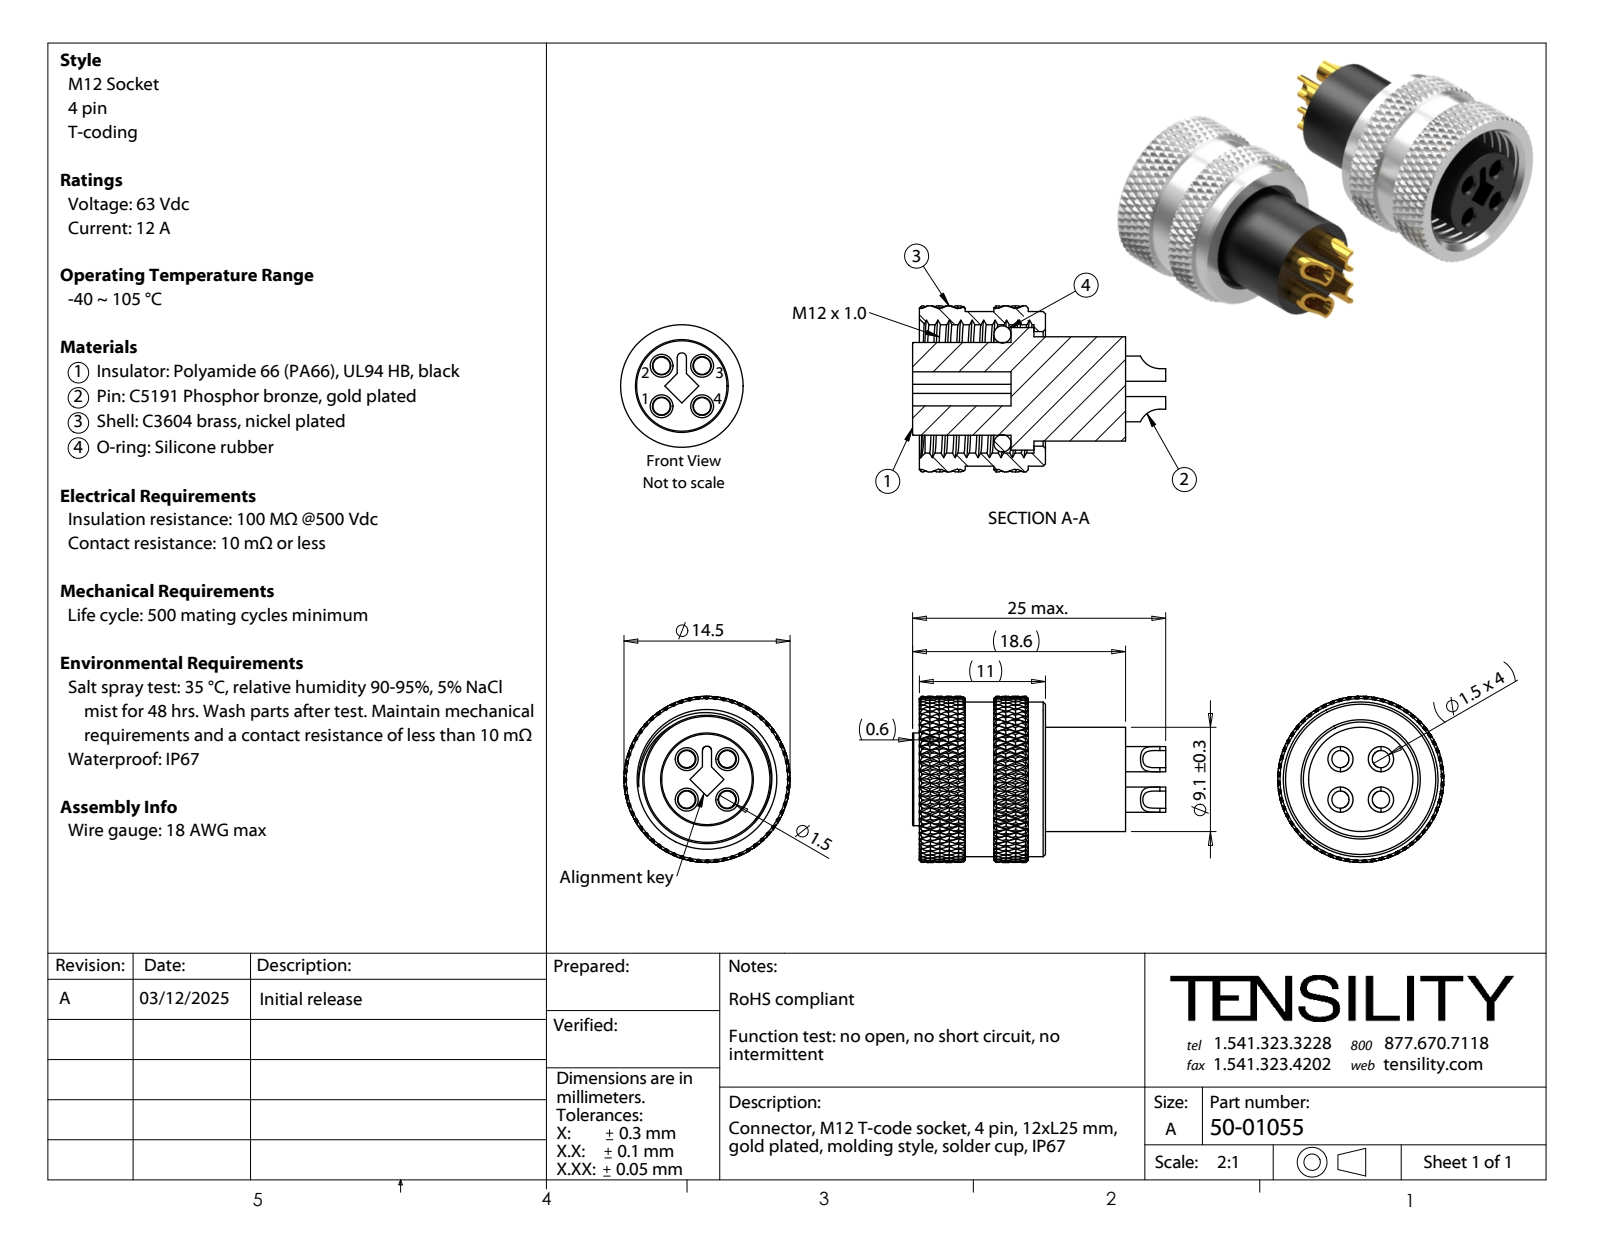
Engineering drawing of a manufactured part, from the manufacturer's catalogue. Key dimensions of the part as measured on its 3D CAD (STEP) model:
Part name (STEP PRODUCT): 50-01055-03; 50-01055-02_step; 50-01055-01; 50-01055 (+1 more)
STEP written by: SolidWorks 2021 (CONFIG_CONTROL_DESIGN)
Units: millimetres
Bodies: 7 solids, 233 faces (74 planar, 97 cylindrical, 62 other)
Overall size (bounding box): 22.1 × 14.5 × 14.5
Volume: 1 718 mm³ · Surface area: 3 338 mm²
Round holes (diameter × count): ⌀1.5 ×4, ⌀1.6 ×4, ⌀10 ×1, ⌀11.2 ×1
Round bosses / shafts (diameter × count): ⌀2.2 ×4, ⌀14.5 ×1, ⌀13.5 ×1, ⌀10.7 ×1, ⌀9.1 ×1, ⌀8.1 ×1
Partial cylindrical surfaces — rounded edges, fillets, slot ends (radius × count): R1.86 ×2, R0.4 ×1
Main face-to-face distances: 8, 10, 2, 7, 3, 1, 11, 18, 1.5, 6
Hole centre spacings: 2.5, 3.54, 5.01
